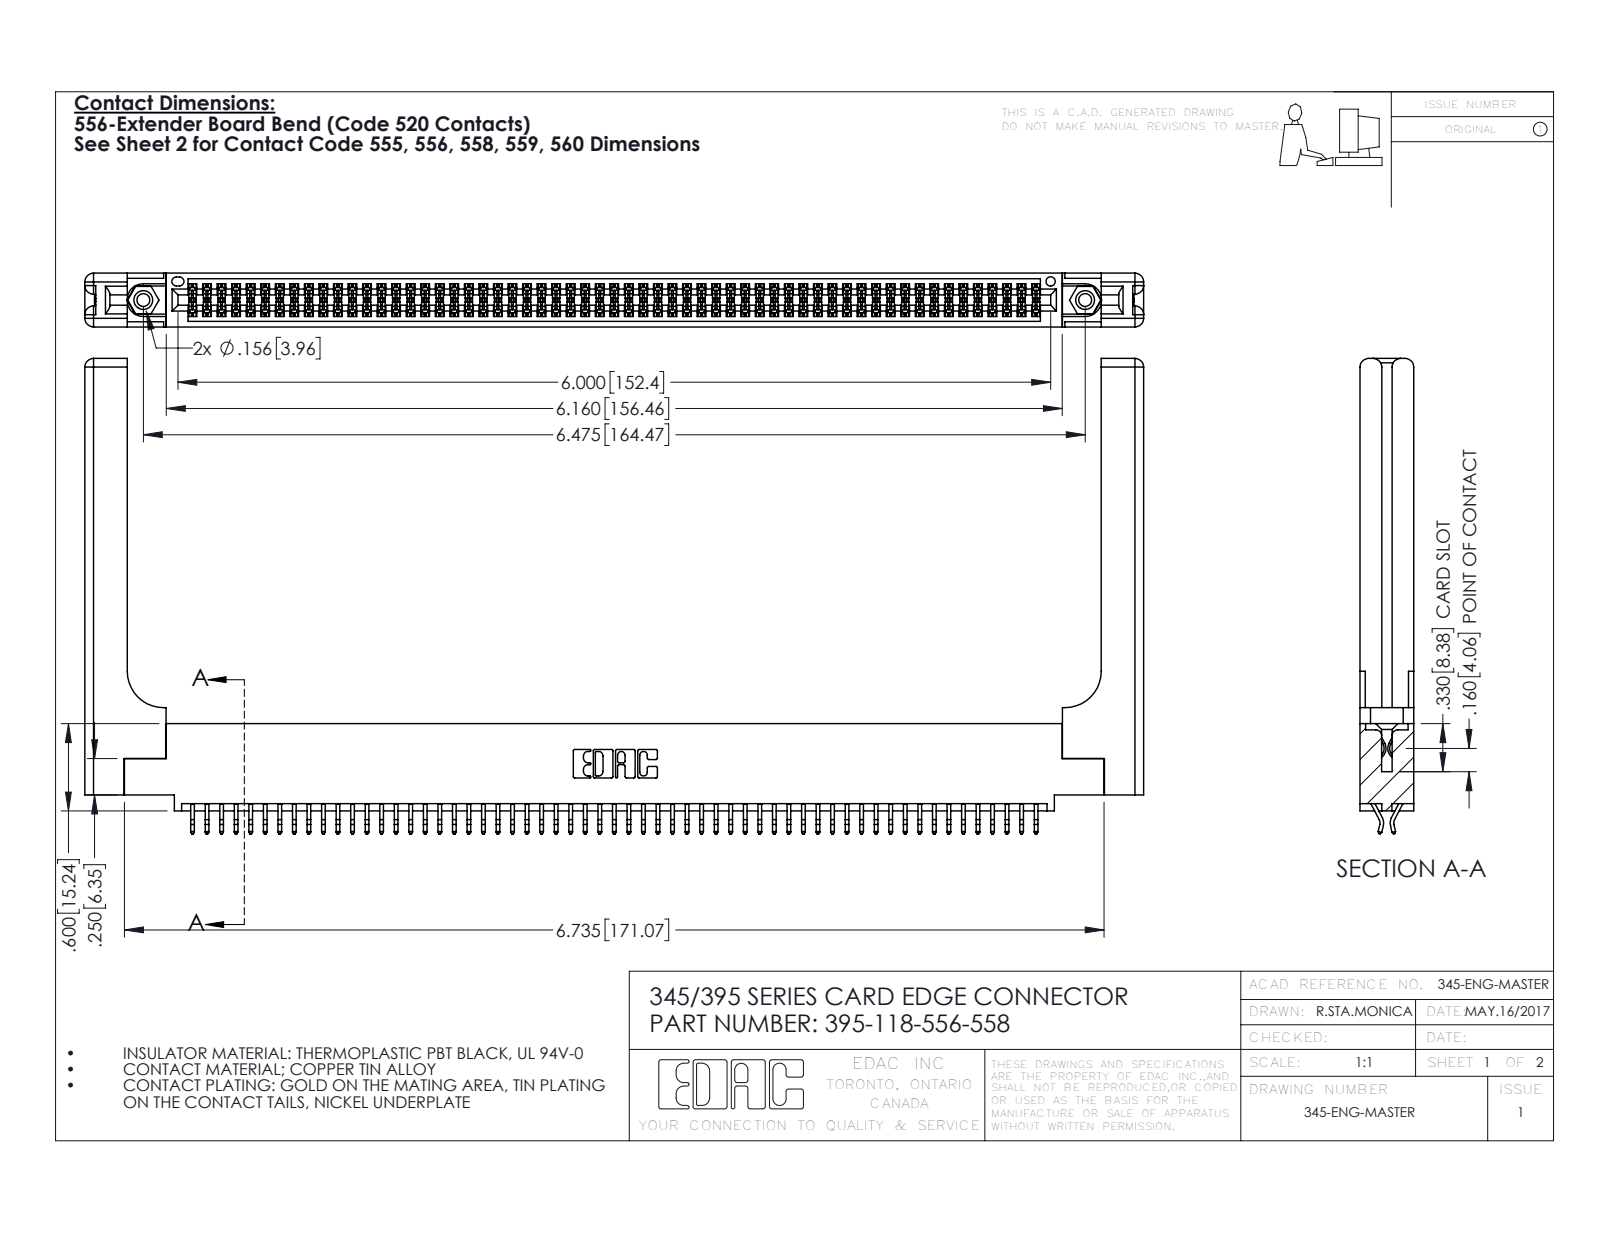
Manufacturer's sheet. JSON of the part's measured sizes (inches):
{"part_name": "345-292-001_556 Tail; 395-118-556-558; 345 Part_0.110 Offset - 0.156 Dia-TH; 345-220-058_345-220-058 (+1 more)", "step_written_by": "SolidWorks 2016 (CONFIG_CONTROL_DESIGN)", "units": "inches", "bodies": {"solids": 123, "faces": 6994, "planar": 4598, "cylindrical": 2336, "other": 60}, "overall_size": [7.279, 3.267, 0.37], "volume_in3": 1.618, "surface_area_in2": 49.67, "round_holes": [[0.089, 2], [0.125, 2], [0.156, 2], [0.064, 1]], "round_bosses_or_shafts": [[0.155, 2]], "partial_cylinders_radius": [[0.006, 177], [0.01, 22], [0.06, 16], [0.007, 6], [0.031, 6], [0.026, 3], [0.01, 2], [0.014, 2]], "face_to_face_distances": [0.072, 0.298, 0.37, 0.025, 0.098, 0.272, 0.2, 0.225, 0.148, 0.15], "hole_center_spacings": [0.27, 6.239, 6.475]}
